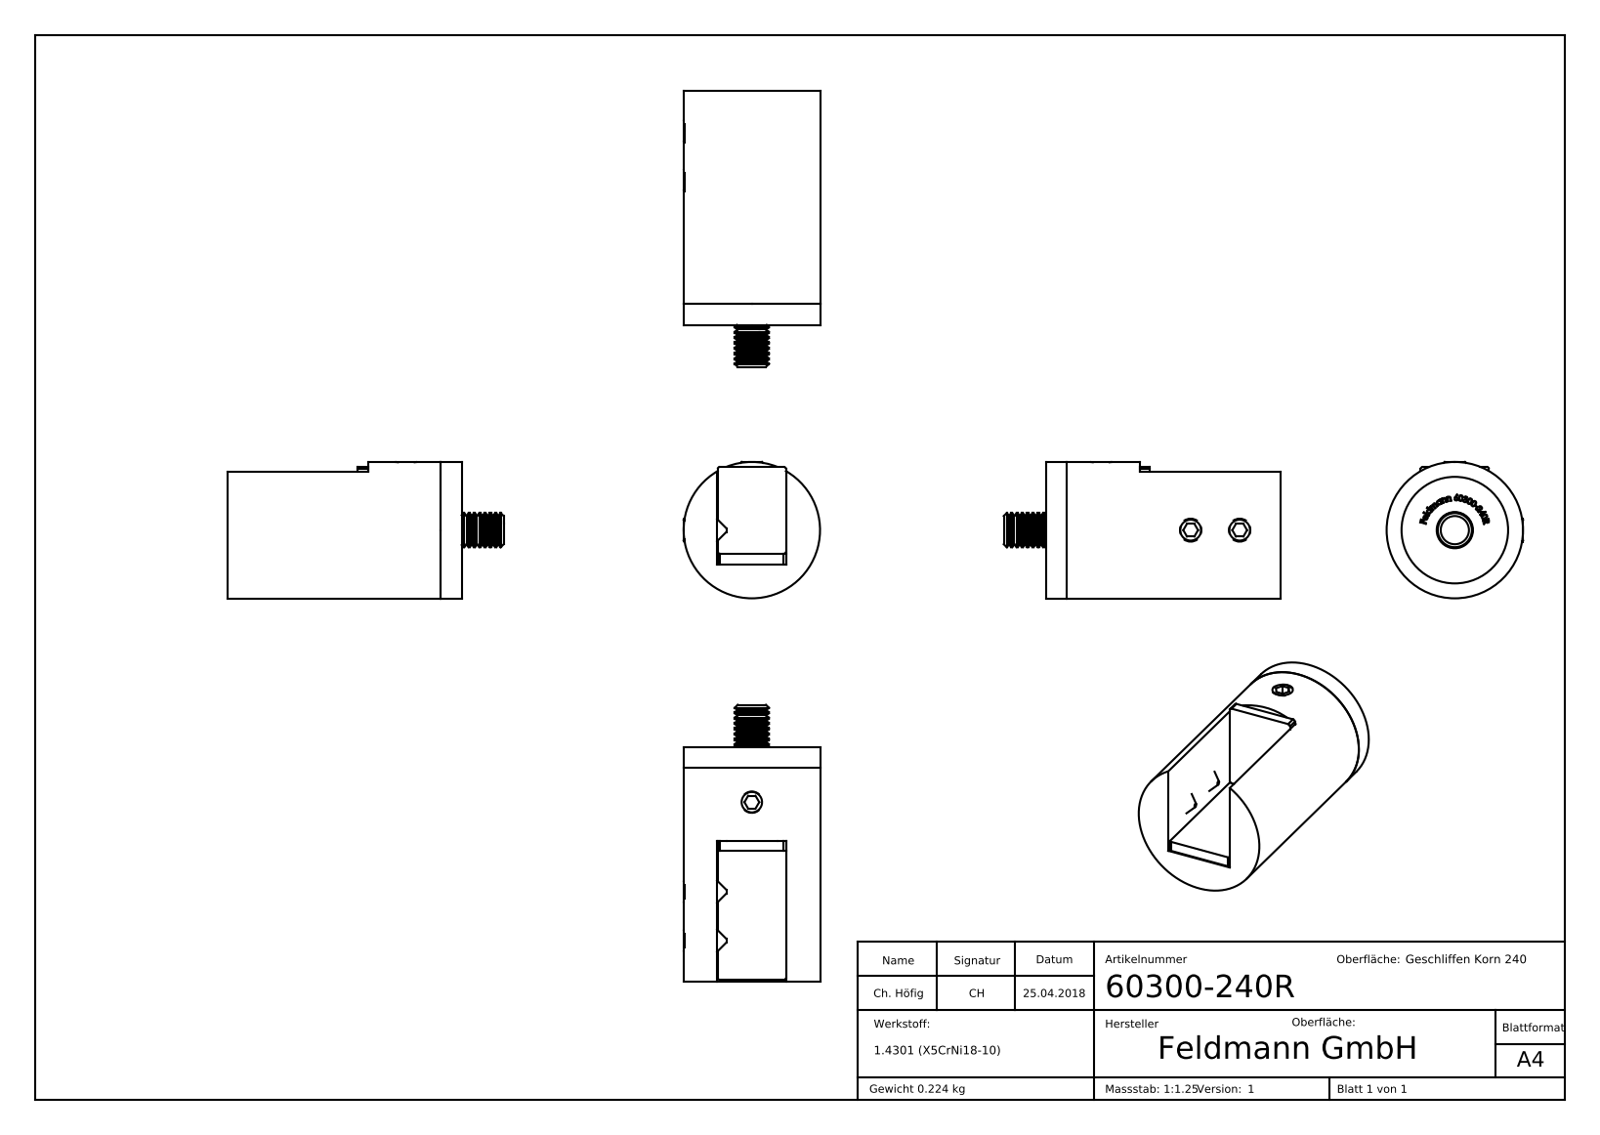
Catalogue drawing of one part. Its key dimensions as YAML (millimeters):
part_name: "6030X-240X Teil4; 6030X-240X Teil2_6030X-240X Teil2; socket countersunk head screw_din_DIN 7991 - M8 x 25 --- 25S; socket set screw cone point_din (+8 more)"
step_written_by: "SolidWorks 2018 (CONFIG_CONTROL_DESIGN)"
units: millimeters
bodies: {solids: 8, faces: 438, planar: 186, cylindrical: 52, other: 200}
overall_size: [70, 64.85, 32]
volume: 31670
surface_area: 16401
round_holes:
  - {diameter: 5, count: 3}
  - {diameter: 8.5, count: 1}
  - {diameter: 25, count: 1}
round_bosses_or_shafts:
  - {diameter: 6, count: 3}
  - {diameter: 32, count: 1}
  - {diameter: 20, count: 1}
  - {diameter: 15.57, count: 1}
  - {diameter: 8, count: 1}
partial_cylinders:
  - {radius: 0.5, count: 8}
face_to_face_distances: [2.45, 16.3, 17, 3.3, 20.3, 53.3, 50, 33, 22.75, 19.45]
hole_center_spacings: [11.5]
